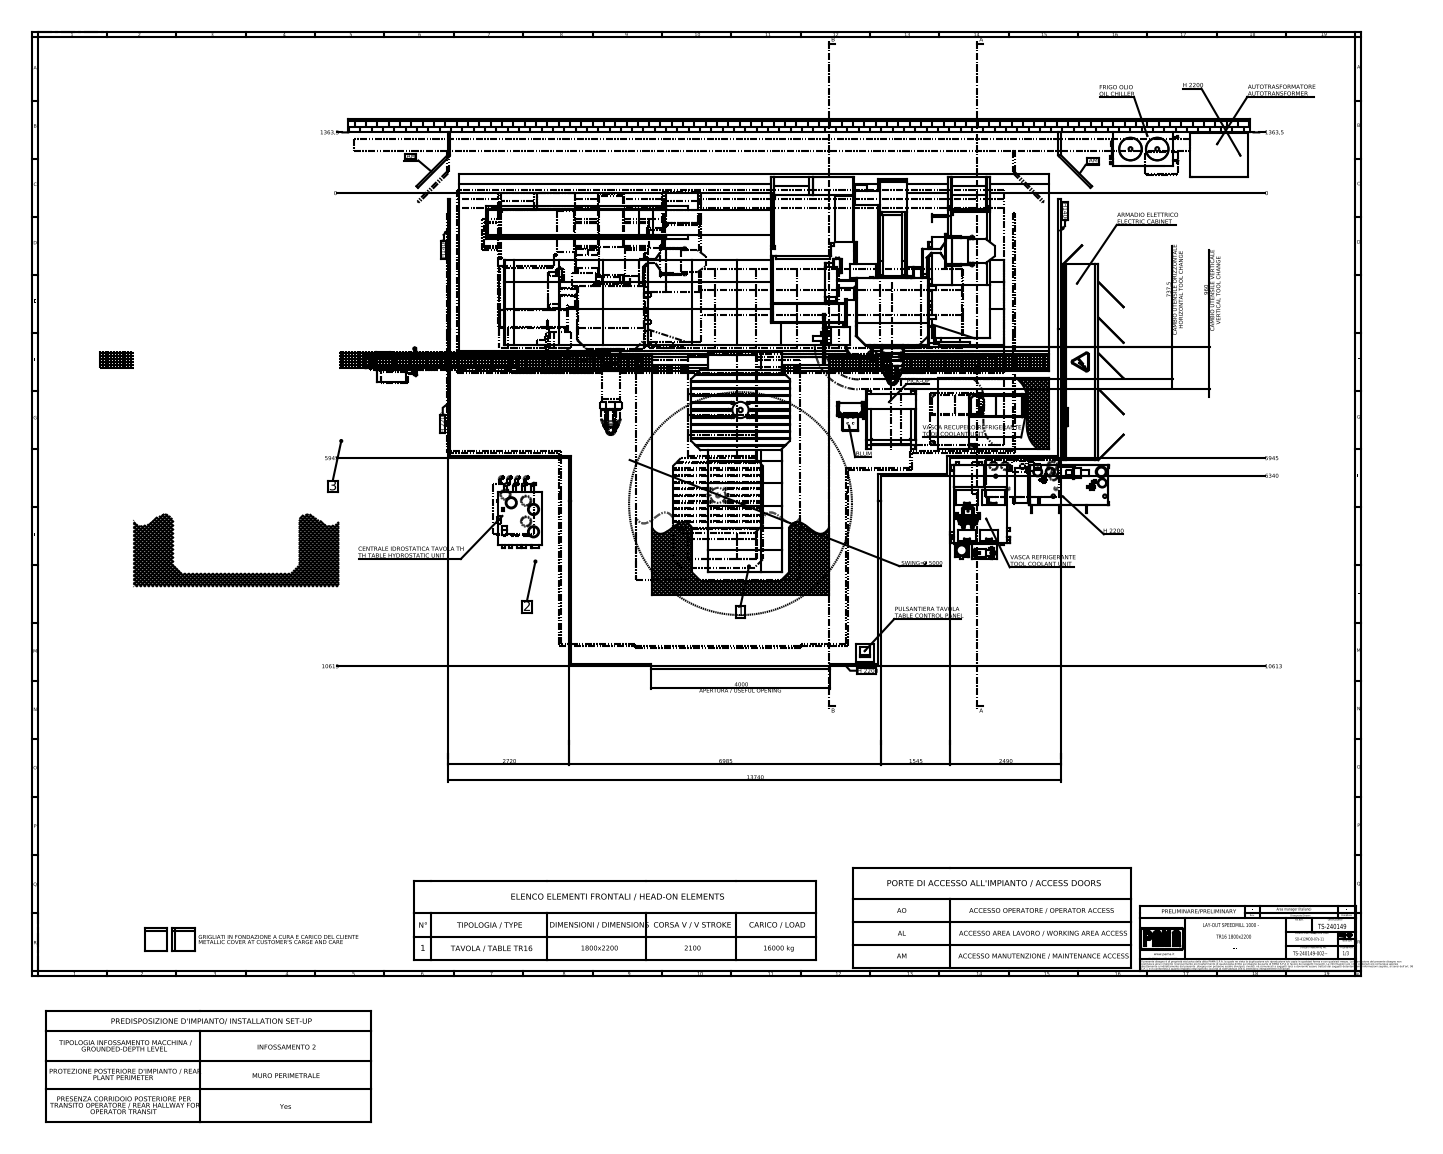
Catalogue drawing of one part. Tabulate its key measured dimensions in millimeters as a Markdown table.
| quantity | value |
| --- | --- |
| part name | S001787_CORSA V=2100; S001789; S001568_1000 L; S003488_MDD Z=1200 (+8 more) |
| STEP written by | SolidWorks 2023 (AUTOMOTIVE_DESIGN) |
| units | millimeters |
| bodies | 488 solids, 7734 faces (5510 planar, 1638 cylindrical, 586 other) |
| overall size | 20240 × 15226.5 × 9400 |
| volume | 621 400 000 000 mm³ |
| surface area | 1 998 000 000 mm² |
| round holes (diameter × count) | 35 × 82, 69.6 × 63, 13 × 8, 14 × 8, 8 × 6, 32 × 6, 12.5 × 4, 50 × 3, 56.66 × 3, 4.2 × 2, 19 × 2, 30 × 2 |
| round bosses / shafts (diameter × count) | 20 × 14, 9 × 10, 30 × 8, 66.3 × 7, 60 × 7, 35 × 6, 200 × 4, 170 × 4 |
| partial cylindrical surfaces (radius × count) | 5 × 238, 15 × 46, 6 × 41, 10 × 27, 35 × 26, 3 × 20, 20 × 20, 8 × 18 |
| main face-to-face distances | 2000, 300, 50, 1340, 660, 15226.5, 14926.5, 20240, 100, 2720 |
| hole center spacings | 250, 500, 750, 1000, 1250, 1500, 1750, 2000 |
